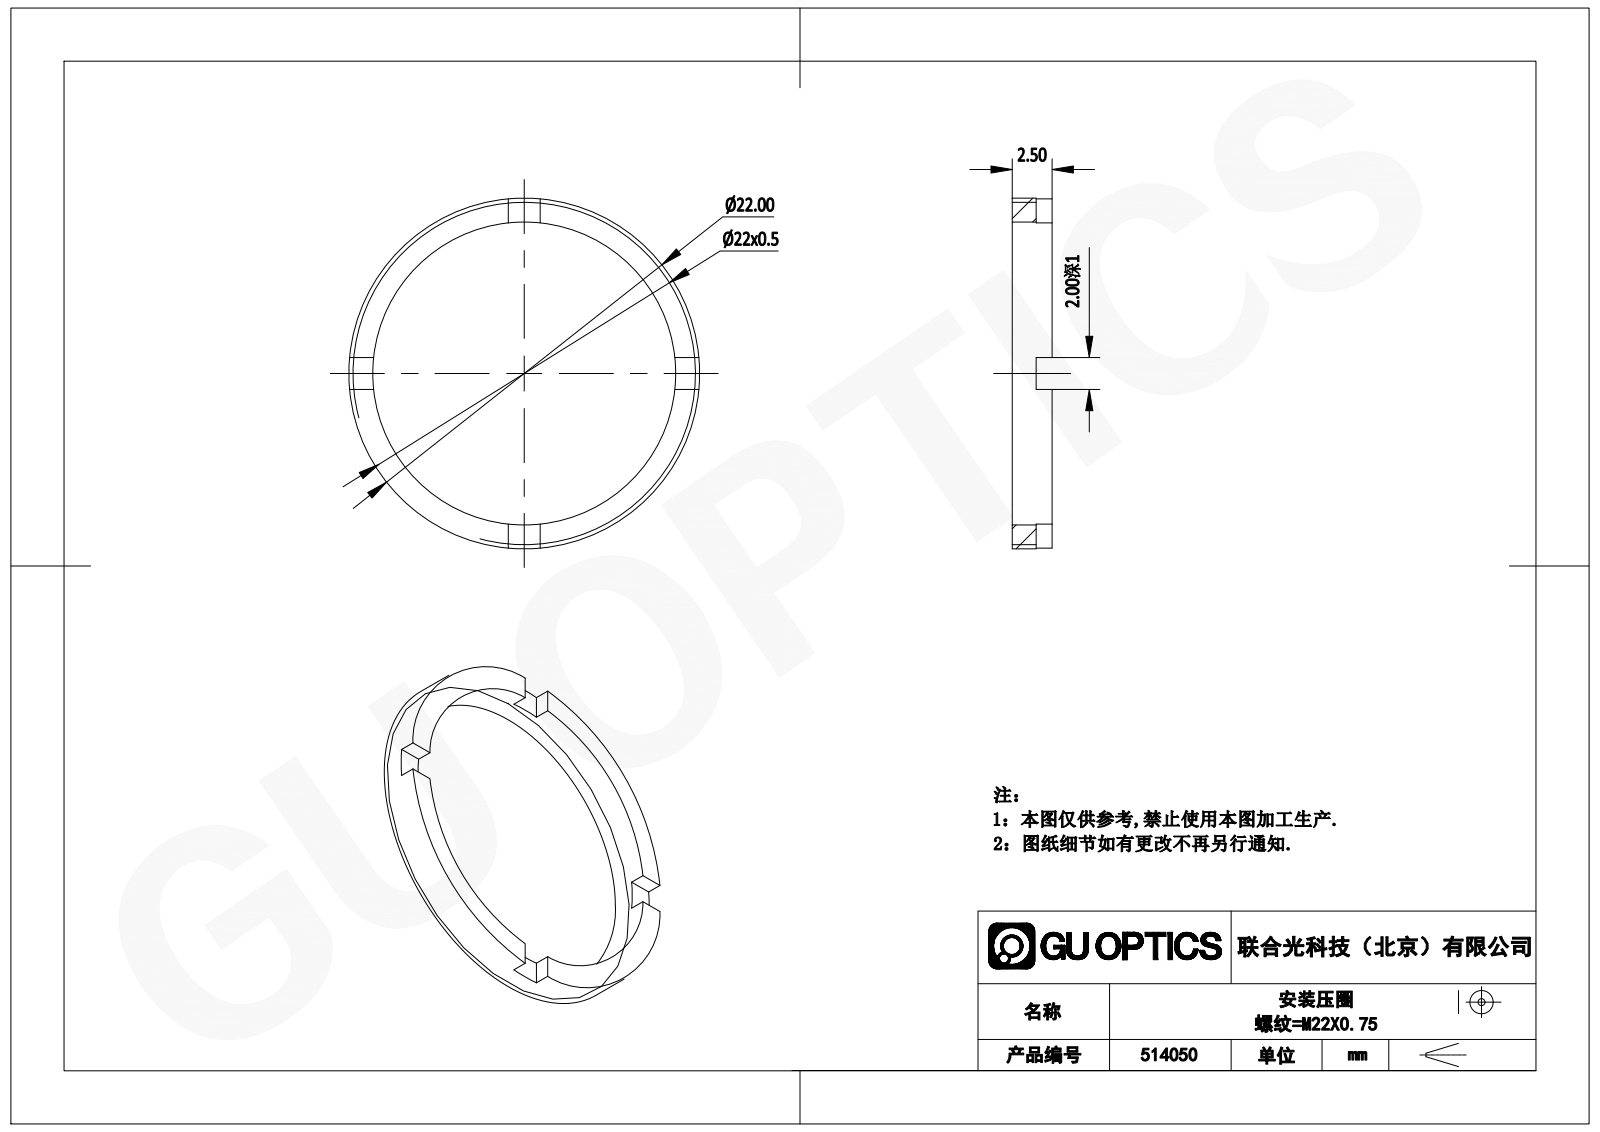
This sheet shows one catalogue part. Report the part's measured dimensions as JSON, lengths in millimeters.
{"part_name": "514050", "step_written_by": "SolidWorks 2020 (CONFIG_CONTROL_DESIGN)", "units": "millimeters", "bodies": {"solids": 1, "faces": 21, "planar": 17, "cylindrical": 4, "other": 0}, "overall_size": [22, 22, 2.5], "volume_mm3": 229, "surface_area_mm2": 511, "round_holes": [[19, 1]], "round_bosses_or_shafts": [[22, 1]], "face_to_face_distances": [2.5, 1.5, 1, 2]}
